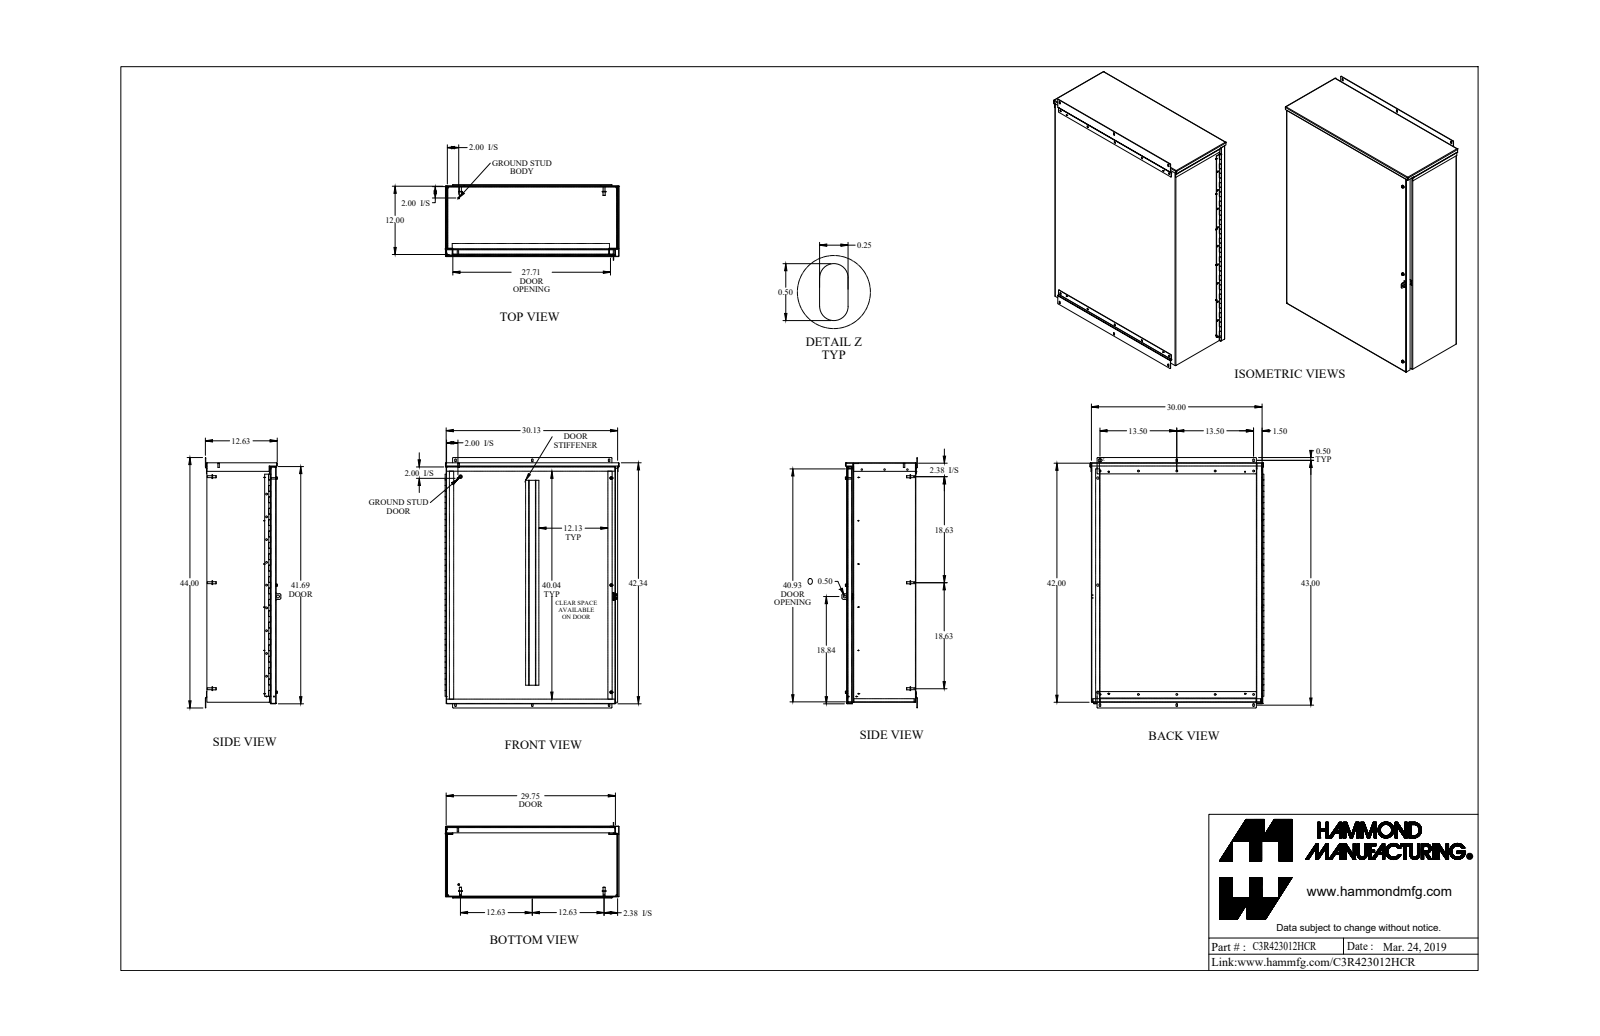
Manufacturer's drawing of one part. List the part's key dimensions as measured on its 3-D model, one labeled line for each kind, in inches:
Part name (STEP PRODUCT): C3R423012HCR_Default
STEP written by: SolidWorks 2019 (CONFIG_CONTROL_DESIGN)
Units: inches
Bodies: 41 solids, 1232 faces (645 planar, 511 cylindrical, 76 other)
Overall size (bounding box): 44 × 30.571 × 13.26
Volume: 391.6 in³ · Surface area: 10 684 in²
Round holes (diameter × count): ⌀0.312 ×10, ⌀0.304 ×9, ⌀0.14 ×4, ⌀0.26 ×4, ⌀0.313 ×4, ⌀0.25 ×3, ⌀0.266 ×3, ⌀0.28 ×3, ⌀0.29 ×3, ⌀0.397 ×3, ⌀0.137 ×2, ⌀0.188 ×1
Round bosses / shafts (diameter × count): ⌀0.131 ×12, ⌀0.65 ×6, ⌀0.375 ×6, ⌀0.33 ×6, ⌀0.51 ×4, ⌀0.244 ×4, ⌀0.187 ×4, ⌀0.5 ×3
Partial cylindrical surfaces — rounded edges, fillets, slot ends (radius × count): R0.036 ×39, R0.108 ×39, R0.125 ×24, R0.171 ×4, R0.25 ×2
Main face-to-face distances: 0.072, 12.1, 12.028, 12.172, 29.928, 42, 30, 29.856, 41.928, 42.072
Hole centre spacings: 4, 6.75, 8, 39.826, 12, 13.5, 16, 24
